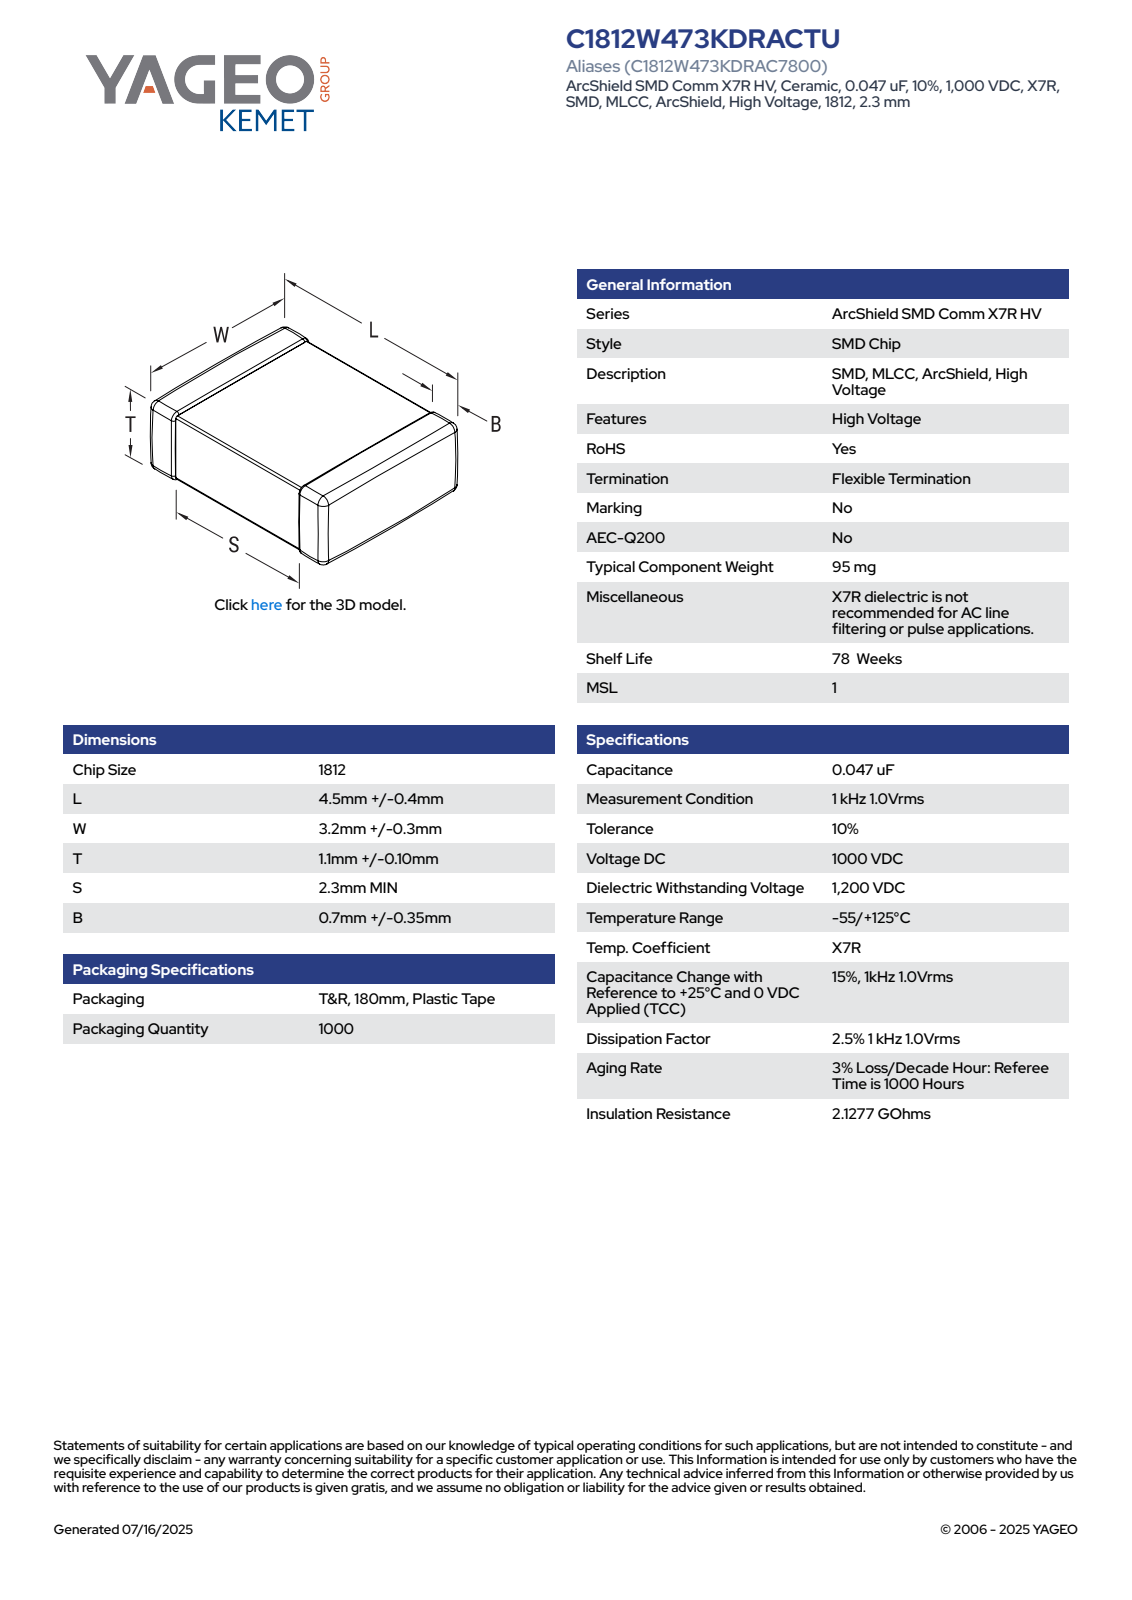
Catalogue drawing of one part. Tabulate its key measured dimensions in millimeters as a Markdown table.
| quantity | value |
| --- | --- |
| part name | CCS_CCSTDNOS_1812_L4.9W3.5T1.2B1.05 |
| STEP written by | SolidWorks 2014 (AUTOMOTIVE_DESIGN) |
| units | millimeters |
| bodies | 4 solids, 125 faces (71 planar, 38 cylindrical, 16 other) |
| overall size | 4.9 × 3.5 × 1.2 |
| volume | 19 mm³ |
| surface area | 53 mm² |
| main face-to-face distances | 1.13, 1.06, 1.2, 3.43, 4.9, 3.36, 3.5, 1.42, 1.94, 1.49 |
